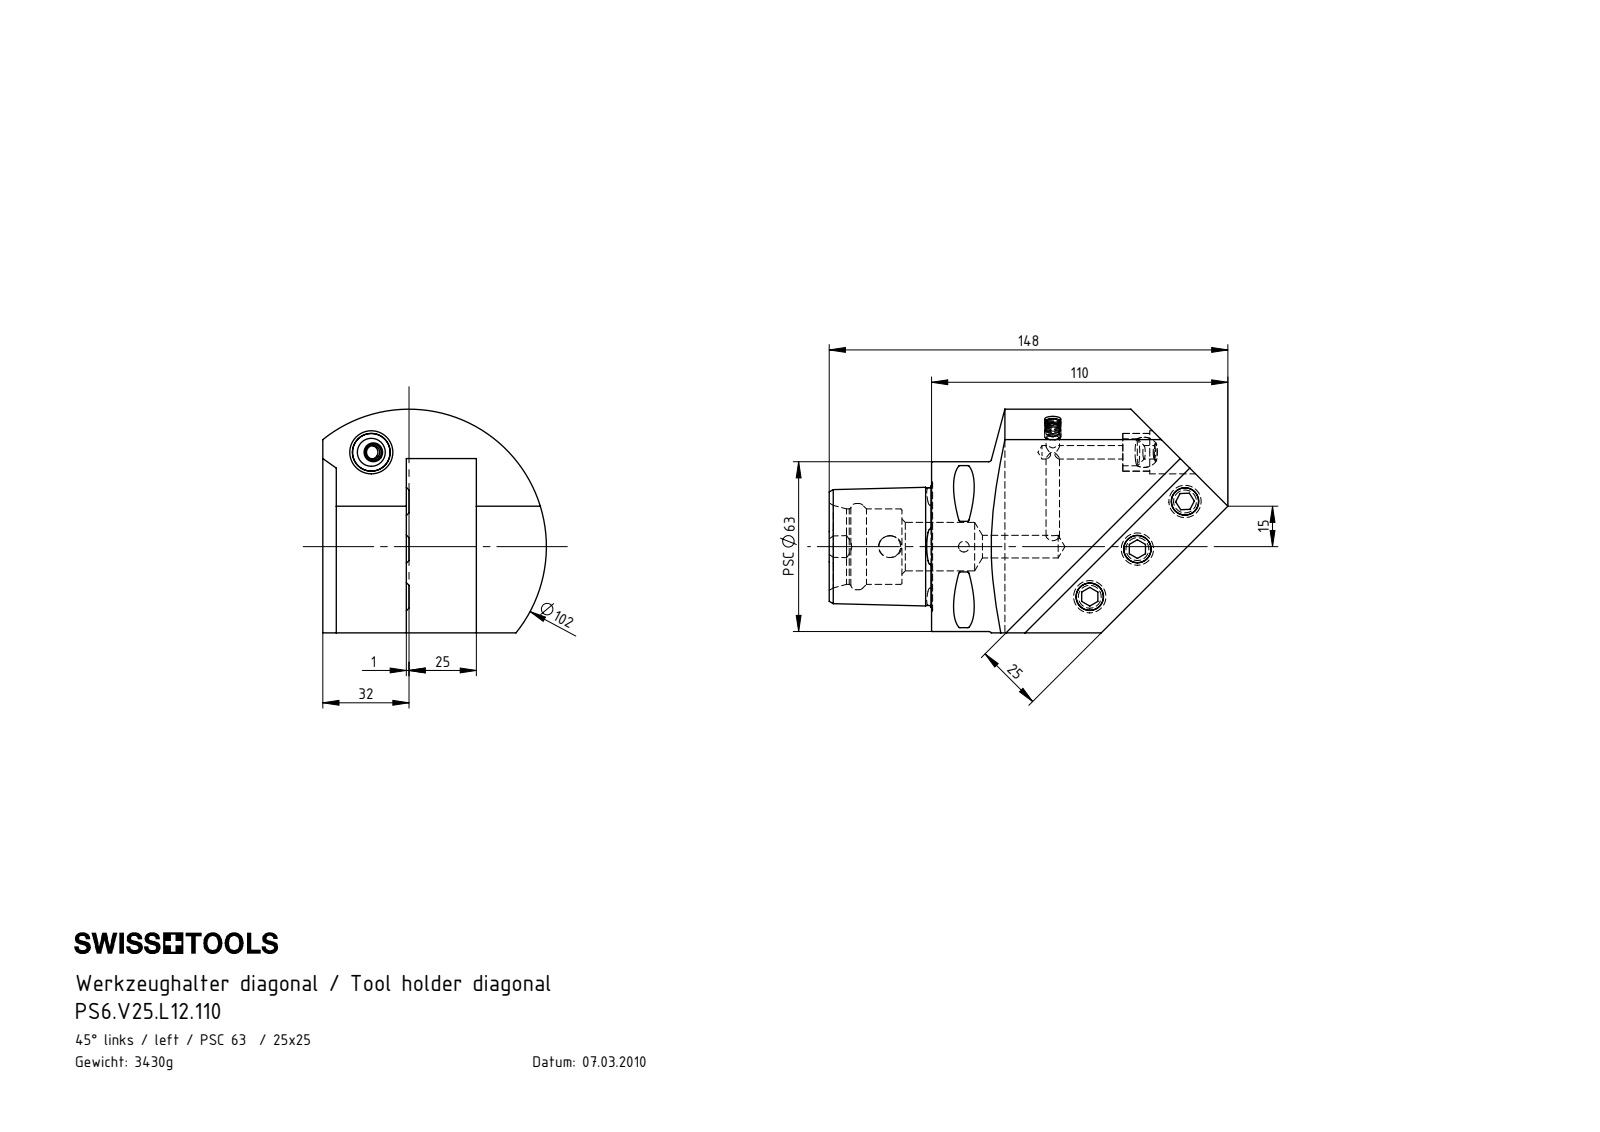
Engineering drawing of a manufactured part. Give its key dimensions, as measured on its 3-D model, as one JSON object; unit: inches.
{"part_name": "KU1-U14.001.012_2; ISO 4026 - M12 x 25_PreviewCfg; KVT_MB_600_060; KU1-U14.001.012_1 (+3 more)", "step_written_by": "SolidWorks 2017 (AUTOMOTIVE_DESIGN)", "units": "inches", "bodies": {"solids": 8, "faces": 256, "planar": 62, "cylindrical": 66, "other": 128}, "overall_size": [5.827, 3.268, 3.268], "volume_in3": 26.7, "surface_area_in2": 89.06, "round_holes": [[0.197, 4], [0.402, 3], [0.157, 1], [0.236, 1], [0.319, 1], [0.331, 1], [0.394, 1], [0.551, 1], [0.63, 1], [0.709, 1], [1.102, 1], [1.26, 1]], "round_bosses_or_shafts": [[0.472, 3], [2.48, 1], [0.236, 1]], "partial_cylinders_radius": [[0.02, 8], [0.031, 1], [0.236, 1], [2.008, 1]], "face_to_face_distances": [1.024, 0.984, 2.244, 1.22, 2.047, 0.197, 1.496, 1.063, 0.984, 0.98], "hole_center_spacings": [0.984, 1.083, 1.484, 1.969, 1.98, 2.536, 3.013, 3.299]}
